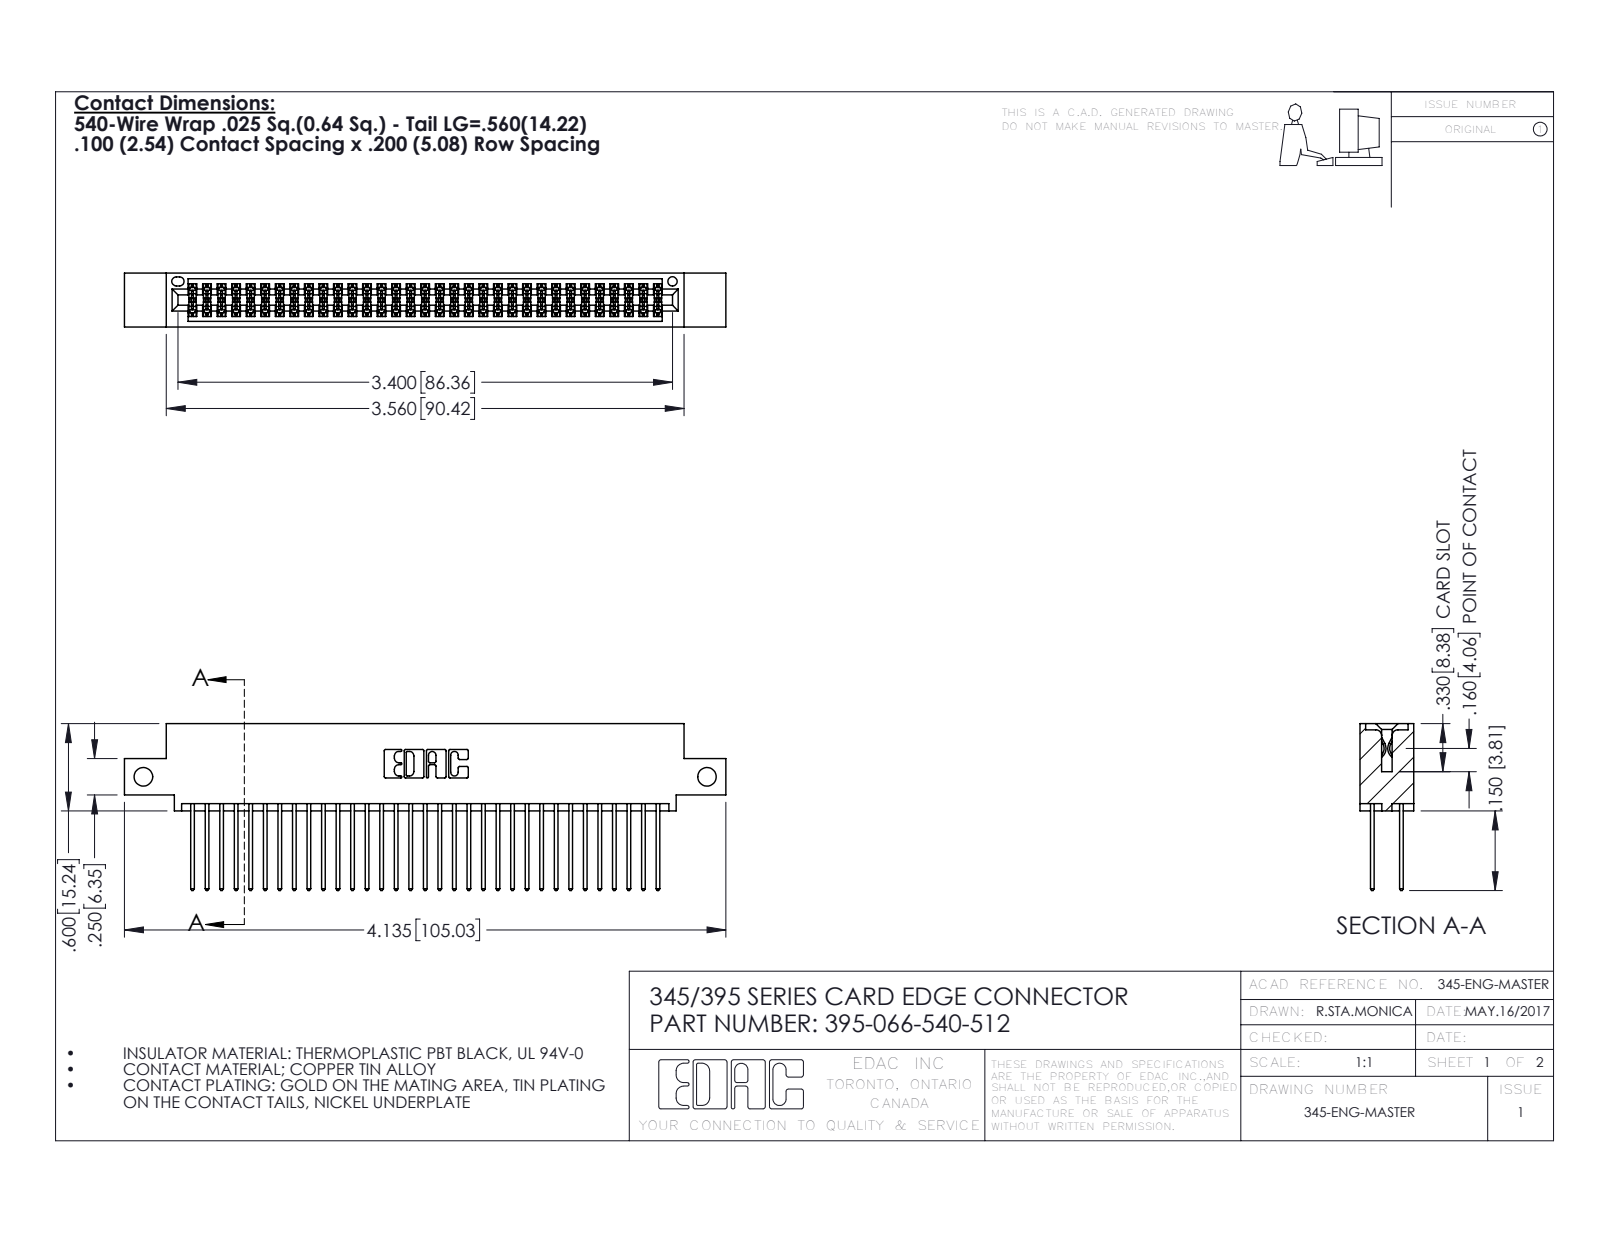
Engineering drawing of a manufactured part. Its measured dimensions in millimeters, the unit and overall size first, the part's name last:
Units: millimetres
Overall size (bounding box): 105 × 29.1 × 9.4
Round holes (diameter × count): ⌀3.3 ×2, ⌀1.6 ×1
Partial cylindrical surfaces — rounded edges, fillets, slot ends (radius × count): R0.2 ×99, R0.3 ×66, R0.3 ×22, R0.2 ×6, R0.8 ×6, R0.7 ×3, R0.4 ×2, R0.5 ×2
Main face-to-face distances: 7.6, 1.8, 5.1, 2.5, 6.9, 0.6, 9.4, 5.7, 4.4, 3.8
Hole centre spacings: 98.4
Volume: 10 200 mm³ · Surface area: 16 030 mm²
Bodies: 67 solids, 3430 faces (2262 planar, 1168 cylindrical, 0 other)
Part name (STEP PRODUCT): 395-066-540-512; 345 Part_0.110 Offset - Side Mount; 345-292-001_345-293-140
STEP written by: SolidWorks 2016 (CONFIG_CONTROL_DESIGN)
